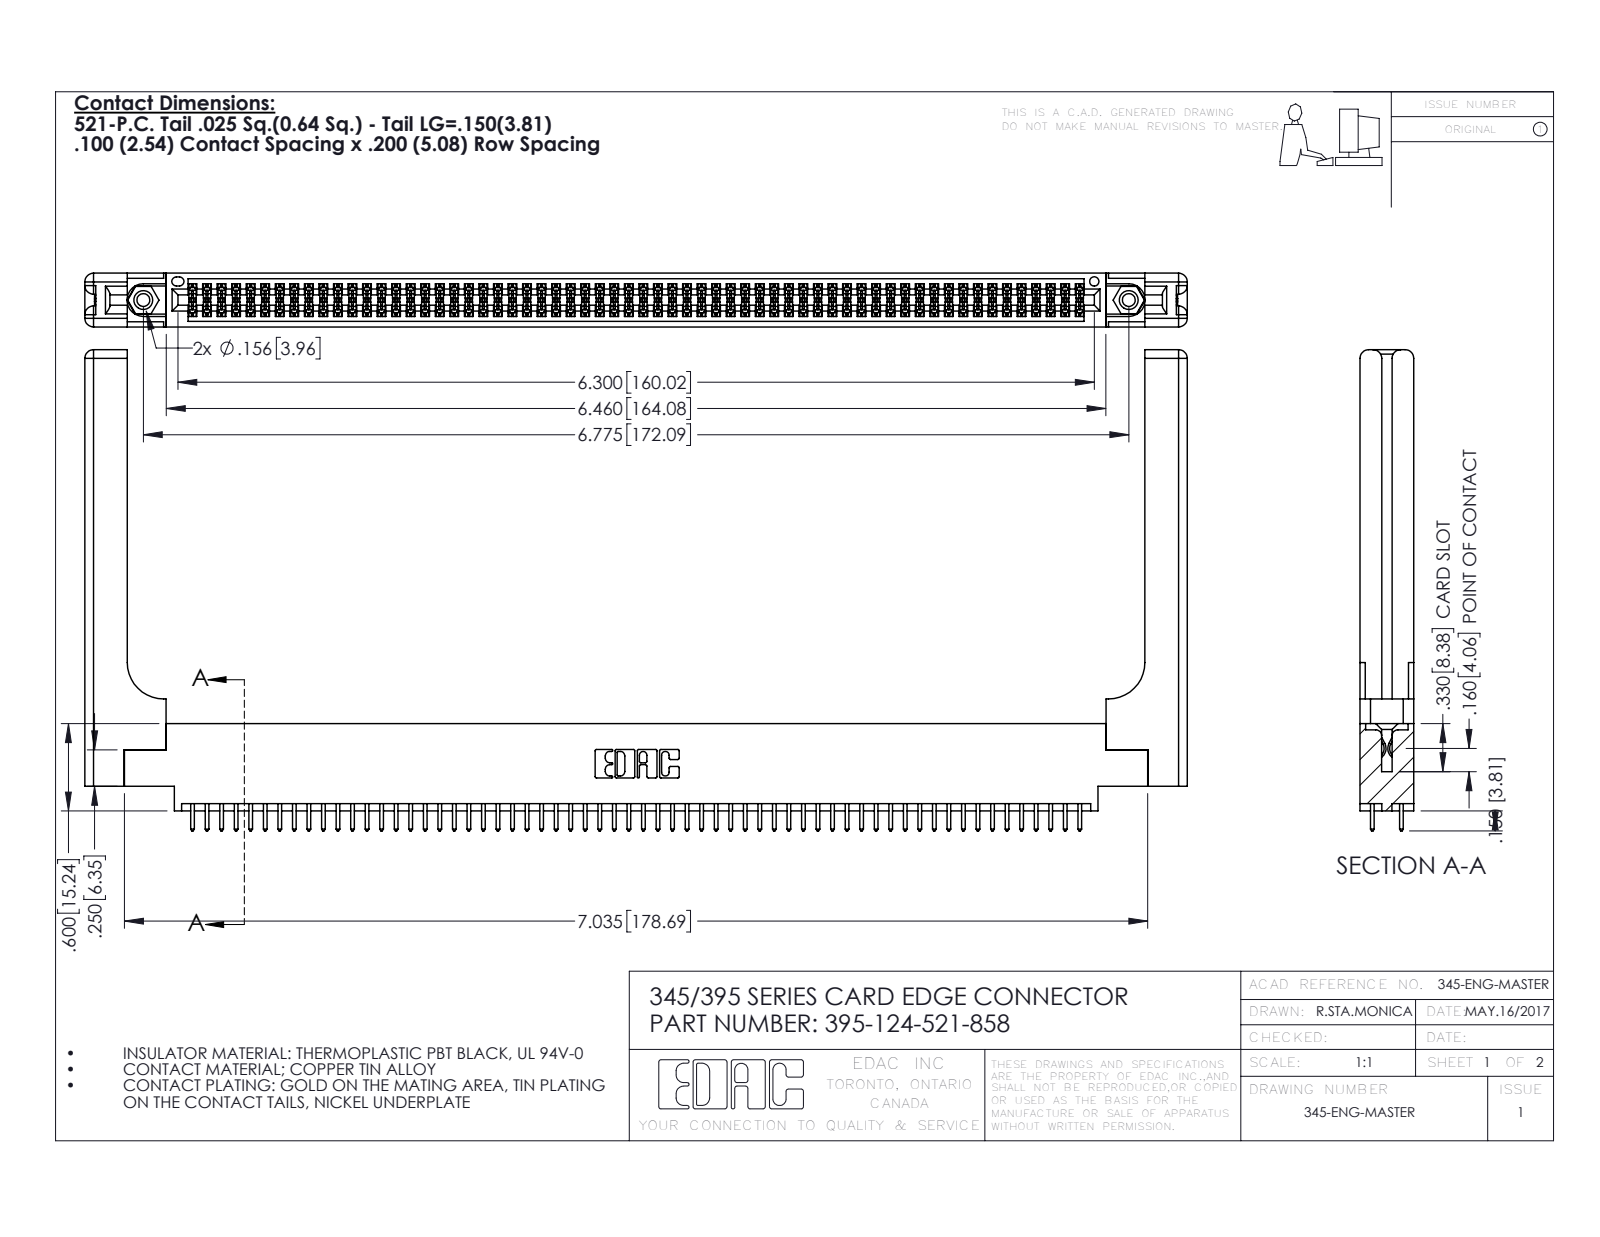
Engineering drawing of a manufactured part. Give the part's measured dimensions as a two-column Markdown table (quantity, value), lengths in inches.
| quantity | value |
| --- | --- |
| part name | 395-124-521-858; 345-250-001_345-250-001-102; 345 Part_0.170 Offset - 0.156 Dia-TH; 345-292-001_345-293-121 (+1 more) |
| STEP written by | SolidWorks 2016 (CONFIG_CONTROL_DESIGN) |
| units | inches |
| bodies | 129 solids, 6586 faces (4324 planar, 2202 cylindrical, 60 other) |
| overall size | 7.579 × 3.307 × 0.37 |
| volume | 1.66 in³ |
| surface area | 51.05 in² |
| round holes (diameter × count) | 0.089 × 2, 0.125 × 2, 0.156 × 2, 0.064 × 1 |
| round bosses / shafts (diameter × count) | 0.155 × 2 |
| partial cylindrical surfaces (radius × count) | 0.006 × 186, 0.01 × 124, 0.01 × 22, 0.06 × 16, 0.007 × 6, 0.031 × 6, 0.026 × 3, 0.014 × 2 |
| main face-to-face distances | 0.072, 0.298, 0.37, 0.098, 0.272, 0.025, 0.2, 0.225, 0.175, 0.15 |
| hole center spacings | 0.27, 6.539, 6.775 |
